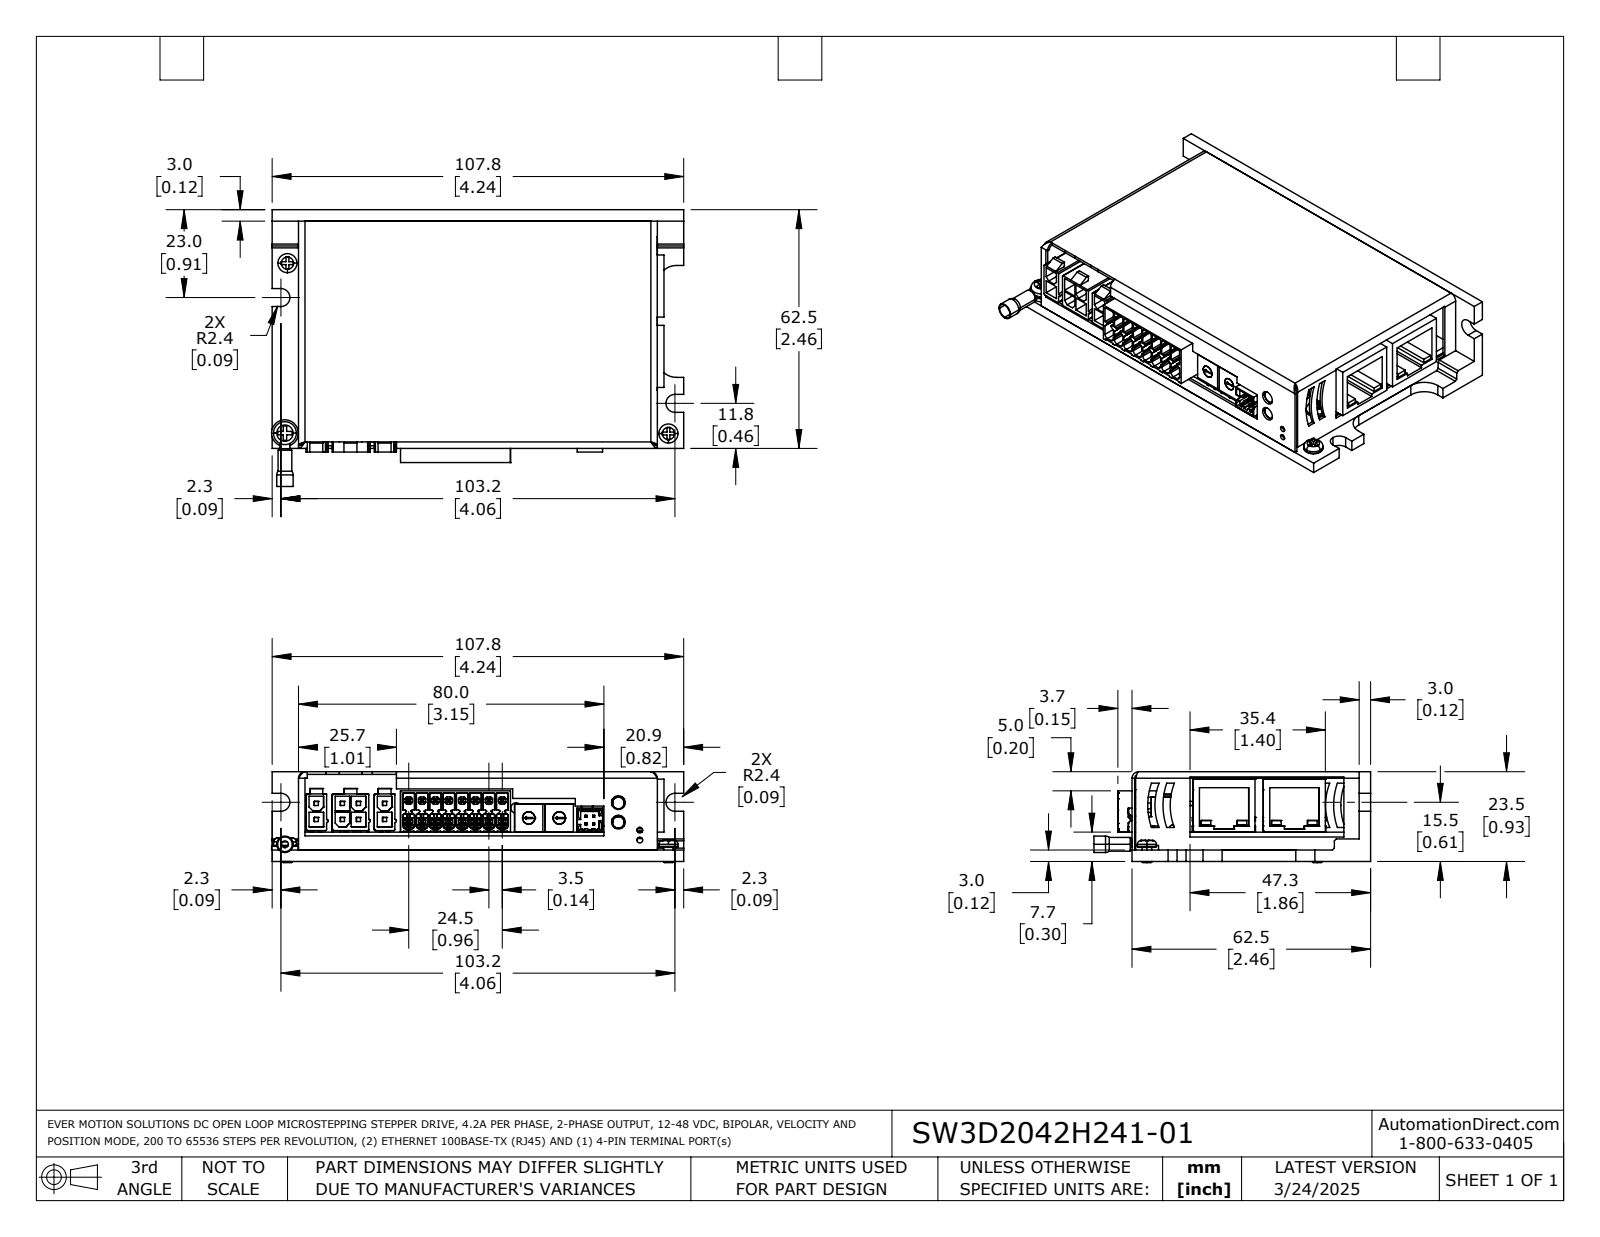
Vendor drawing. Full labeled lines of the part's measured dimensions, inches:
Part name (STEP PRODUCT): SW3D2042H241-01C0680
STEP written by: SolidWorks 2021 (AUTOMOTIVE_DESIGN)
Units: inches
Bodies: 21 solids, 3055 faces (2002 planar, 837 cylindrical, 216 other)
Overall size (bounding box): 4.25 × 2.853 × 0.937
Volume: 3.2 in³ · Surface area: 95.32 in²
Round holes (diameter × count): ⌀0.03 ×22, ⌀0.035 ×16, ⌀0.055 ×16, ⌀0.071 ×9, ⌀0.04 ×8, ⌀0.126 ×5, ⌀0.035 ×4, ⌀0.063 ×4, ⌀0.106 ×4, ⌀0.118 ×4, ⌀0.098 ×3, ⌀0.05 ×2
Round bosses / shafts (diameter × count): ⌀0.197 ×3, ⌀0.162 ×2, ⌀0.148 ×2, ⌀0.126 ×2, ⌀0.12 ×2, ⌀0.098 ×2, ⌀0.276 ×1, ⌀0.236 ×1
Partial cylindrical surfaces — rounded edges, fillets, slot ends (radius × count): R0.004 ×144, R0.012 ×19, R0.008 ×18, R0.035 ×16, R0.006 ×12, R0.006 ×10, R0.63 ×7, R0.703 ×7
Main face-to-face distances: 0.118, 0.028, 0.925, 0.807, 0.898, 0.78, 0.121, 0.686, 0.302, 0.184
Hole centre spacings: 0.112, 0.1, 0.18, 0.2, 0.269, 0.725, 0.108, 0.117
